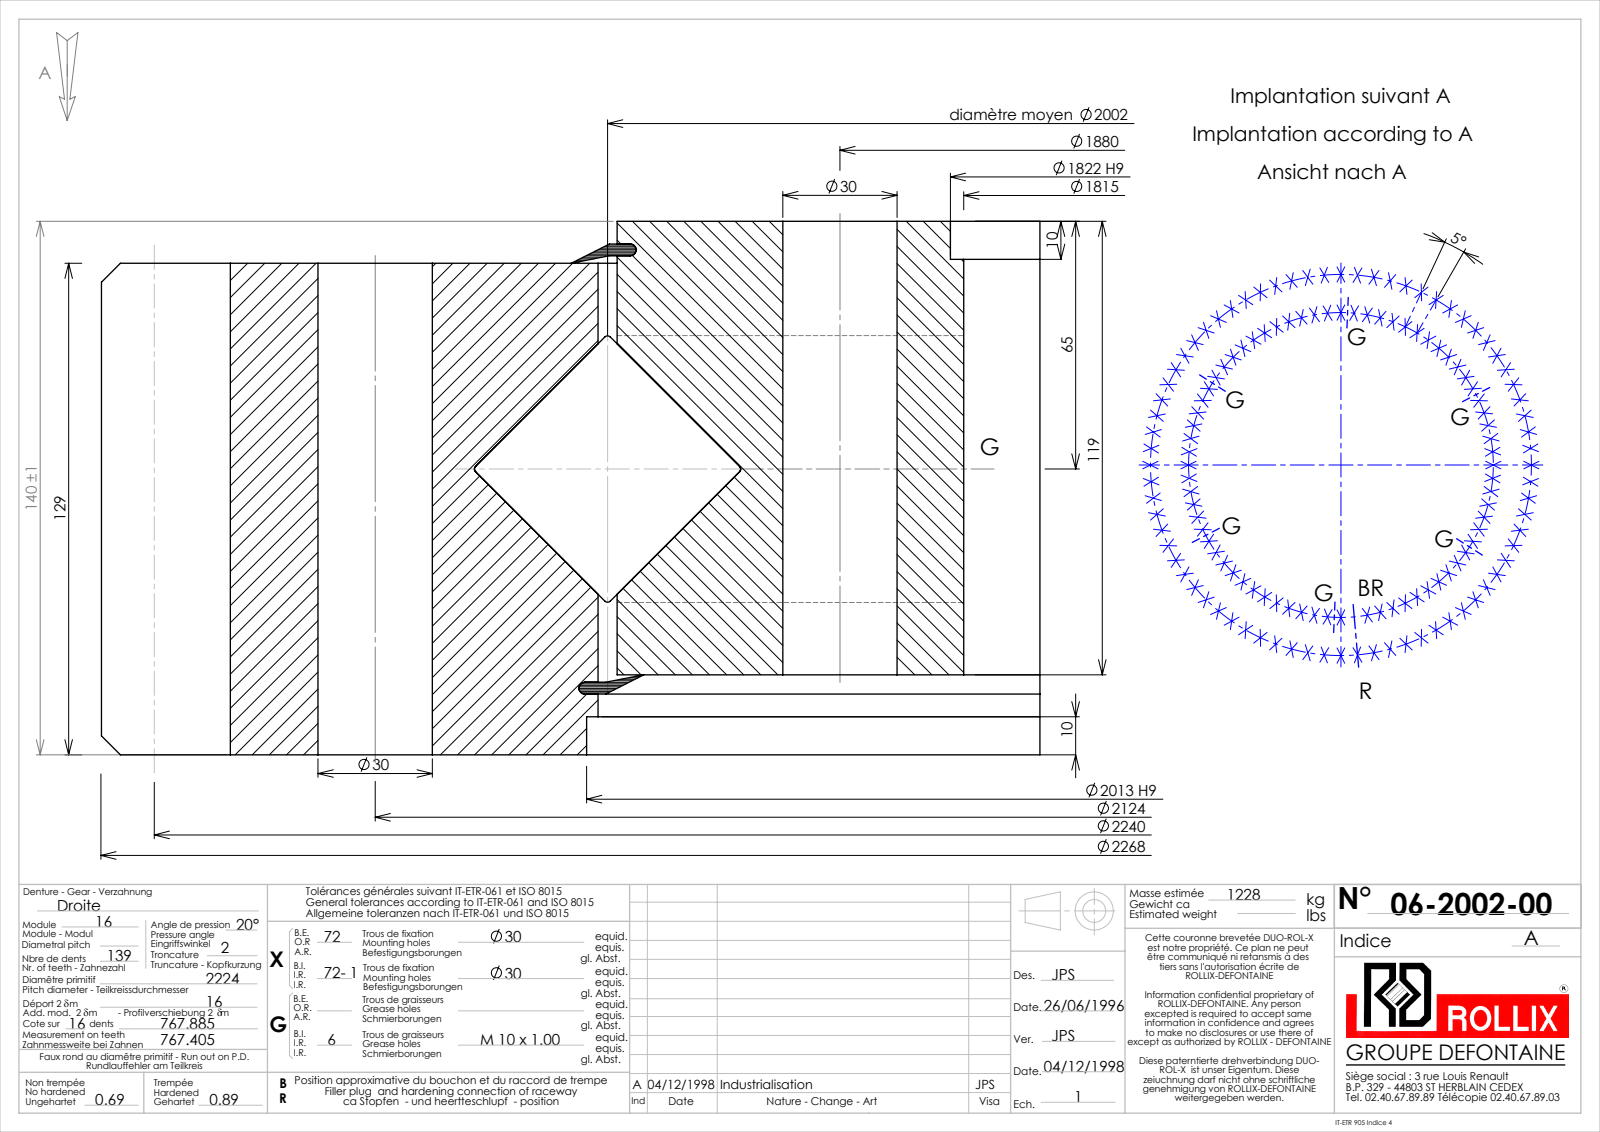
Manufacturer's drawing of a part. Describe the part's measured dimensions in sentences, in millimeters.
The part is named "06-2002-00". Its 3-D file was written by "SolidWorks 2016 (CONFIG_CONTROL_DESIGN)". It is 5 solids with 1218 faces: 294 planar, 597 cylindrical and 327 other. Overall it measures 2267.98 by 2267.86 by 140 millimeters. Its volume is 137 600 000 cubic millimeters and its surface area 9 017 000 square millimeters. Round holes: 143 of diameter 30, 6 of diameter 9, 1 of diameter 1815, 1 of diameter 1822, 1 of diameter 2007, 1 of diameter 2013. Round bosses or shafts: 1 of diameter 1997, 1 of diameter 50. Partial cylindrical surfaces (rounded edges, fillets, slot ends): 1 of radius 1100, 1 of radius 1134. The main face-to-face distances are 129, 21, 108, 11, 119, 140, 1.95, 109.95, 3.1, 5.05. The hole center spacings are 368.83, 812.82, 92.65, 549.73, 277.24, 459.72, 185.12, 726.45.
